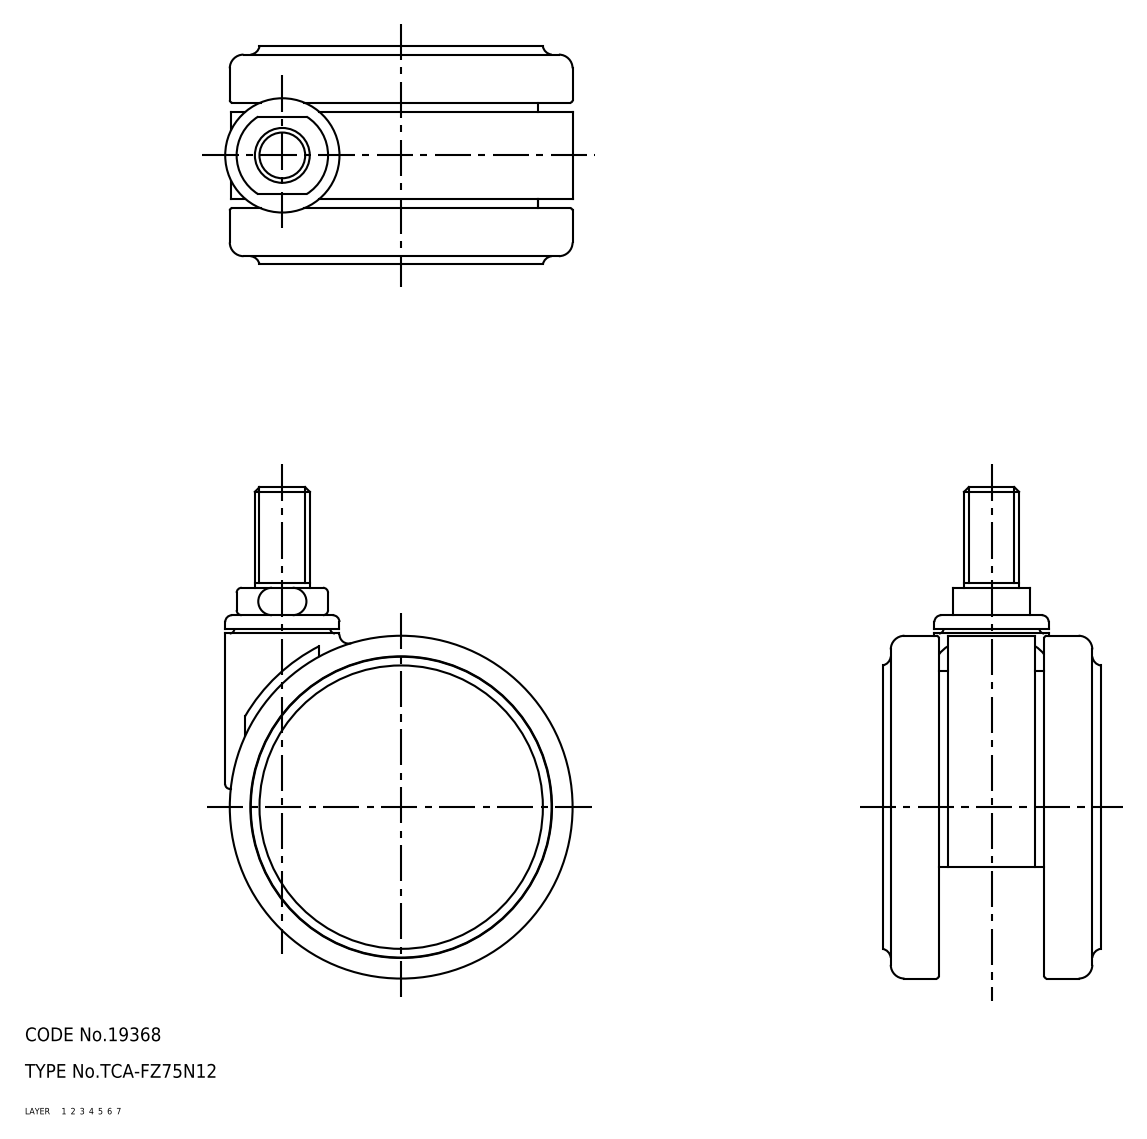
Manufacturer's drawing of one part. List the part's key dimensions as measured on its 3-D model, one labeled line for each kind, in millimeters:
Part name (STEP PRODUCT): caster; TCA-FZ75N12
STEP written by: SolidWorks 2015 (AUTOMOTIVE_DESIGN)
Units: millimetres
Bodies: 1 solid, 1801 faces (425 planar, 766 cylindrical, 610 other)
Overall size (bounding box): 107.5 × 76 × 47.7
Volume: 114 116 mm³ · Surface area: 69 096 mm²
Round holes (diameter × count): ⌀6.5 ×1, ⌀8 ×1, ⌀8.1 ×1, ⌀8.5 ×1, ⌀10.2 ×1, ⌀11 ×1, ⌀17 ×1, ⌀18.1 ×1, ⌀19 ×1, ⌀22.6 ×1, ⌀59 ×1, ⌀63 ×1
Round bosses / shafts (diameter × count): ⌀16 ×2, ⌀65.8 ×1, ⌀54 ×1, ⌀26 ×1, ⌀25 ×1, ⌀14 ×1, ⌀12 ×1, ⌀10 ×1
Partial cylindrical surfaces — rounded edges, fillets, slot ends (radius × count): R0.5 ×119, R1 ×79, R0.3 ×60, R0.2 ×16, R2 ×12, R3 ×1, R4 ×1, R6 ×1
Main face-to-face distances: 1.5, 46.2, 1.8, 3.3, 44.4, 42.9, 32.1, 9, 35.4, 12.3
